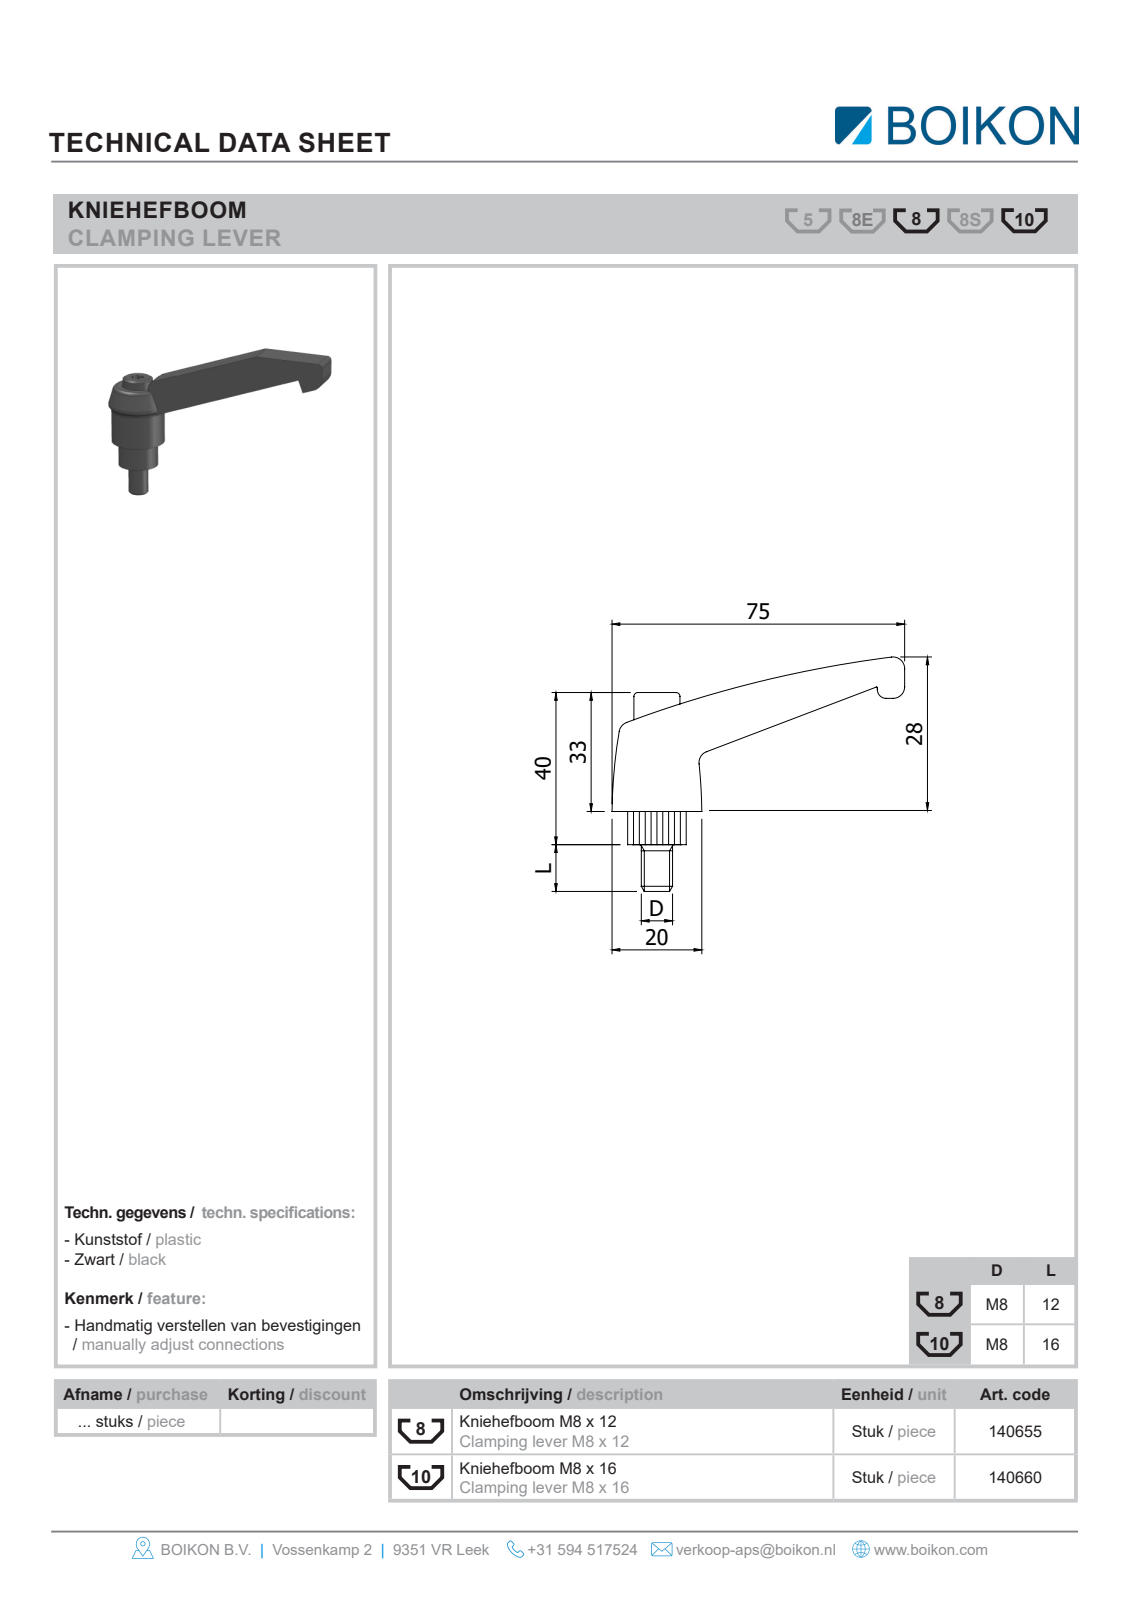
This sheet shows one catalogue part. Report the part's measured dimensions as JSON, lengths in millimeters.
{"part_name": "Root; 140660Kniehefboom M8x16BOIKON", "step_written_by": "HiCAD 2013 1802.4 Build 509 (AUTOMOTIVE_DESIGN)", "units": "millimeters", "bodies": {"solids": 1, "faces": 67, "planar": 32, "cylindrical": 29, "other": 6}, "overall_size": [91.88, 69.5, 23.75], "volume_mm3": 15917, "surface_area_mm2": 9582, "round_holes": [[9.6, 1], [12.8, 1]], "round_bosses_or_shafts": [[21.5, 1], [16, 1], [12.16, 1], [11.2, 1], [8, 1]], "partial_cylinders_radius": [[0.56, 6], [0.98, 6], [3.2, 4], [0.8, 2], [1.6, 1], [3.7, 1], [4.8, 1]], "face_to_face_distances": [1.6, 9.4, 11, 7.8, 43.5, 10, 53.5, 51.9, 41.9, 33.3]}
